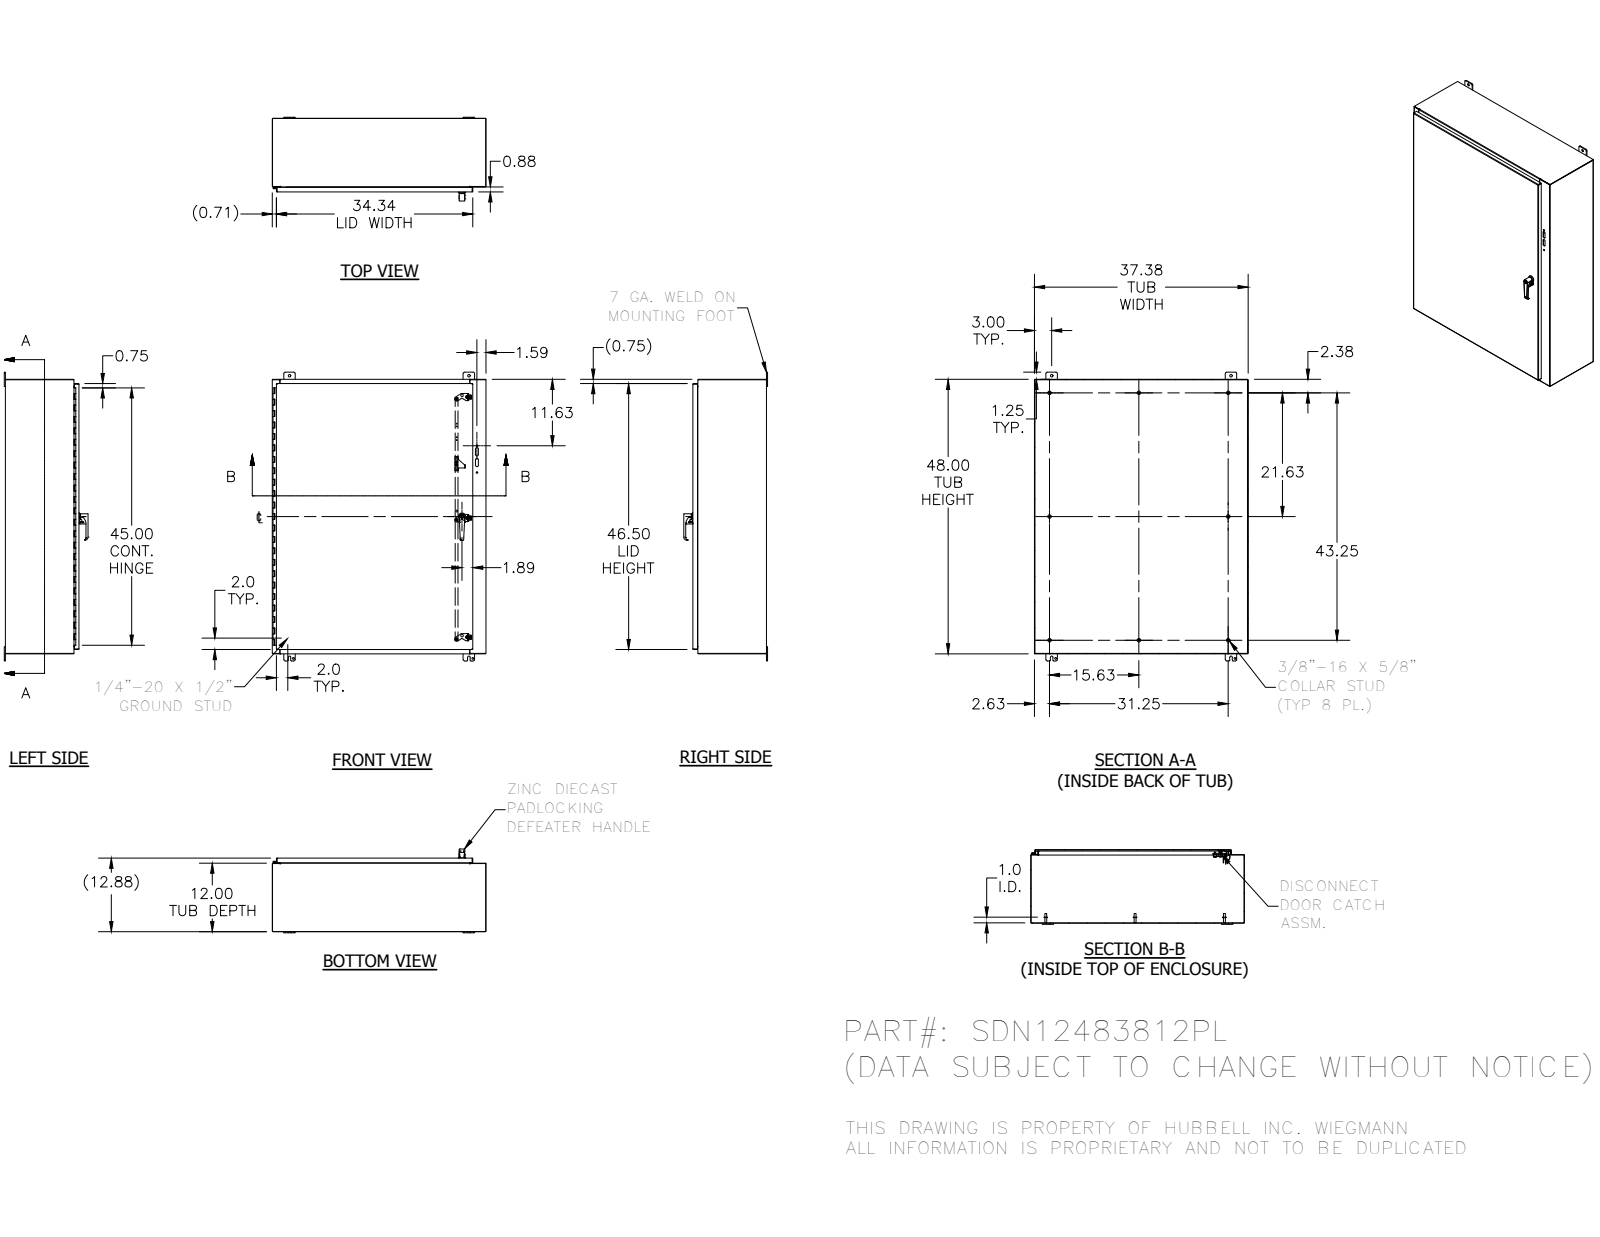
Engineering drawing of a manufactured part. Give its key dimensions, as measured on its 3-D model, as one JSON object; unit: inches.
{"part_name": "SDN12483812PL; SDN12483812PLBLR; 3889; 34840 (+8 more)", "step_written_by": "Autodesk Inventor 2012 (AUTOMOTIVE_DESIGN)", "units": "inches", "bodies": {"solids": 64, "faces": 1889, "planar": 1012, "cylindrical": 623, "other": 254}, "overall_size": [50.5, 37.375, 14.649], "volume_in3": 459.3, "surface_area_in2": 12332, "round_holes": [[0.145, 6], [0.313, 4], [0.32, 4], [0.438, 4], [0.196, 3], [0.211, 3], [0.22, 3], [0.313, 3], [0.45, 3], [0.156, 2], [0.281, 2], [0.307, 2]], "round_bosses_or_shafts": [[0.625, 10], [0.33, 10], [0.437, 6], [0.3, 6], [0.225, 6], [0.25, 4], [0.19, 4], [0.75, 3]], "partial_cylinders_radius": [[0.02, 38], [0.012, 31], [0.025, 24], [0.25, 23], [0.125, 21], [0.031, 18], [0.105, 18], [0.094, 6]], "face_to_face_distances": [0.074, 12.801, 12.727, 12.875, 37.301, 47.926, 37.227, 37.375, 11.926, 0.875], "hole_center_spacings": [42, 20.844, 21.156, 1.593, 31.375, 48, 57.344, 0.5]}
